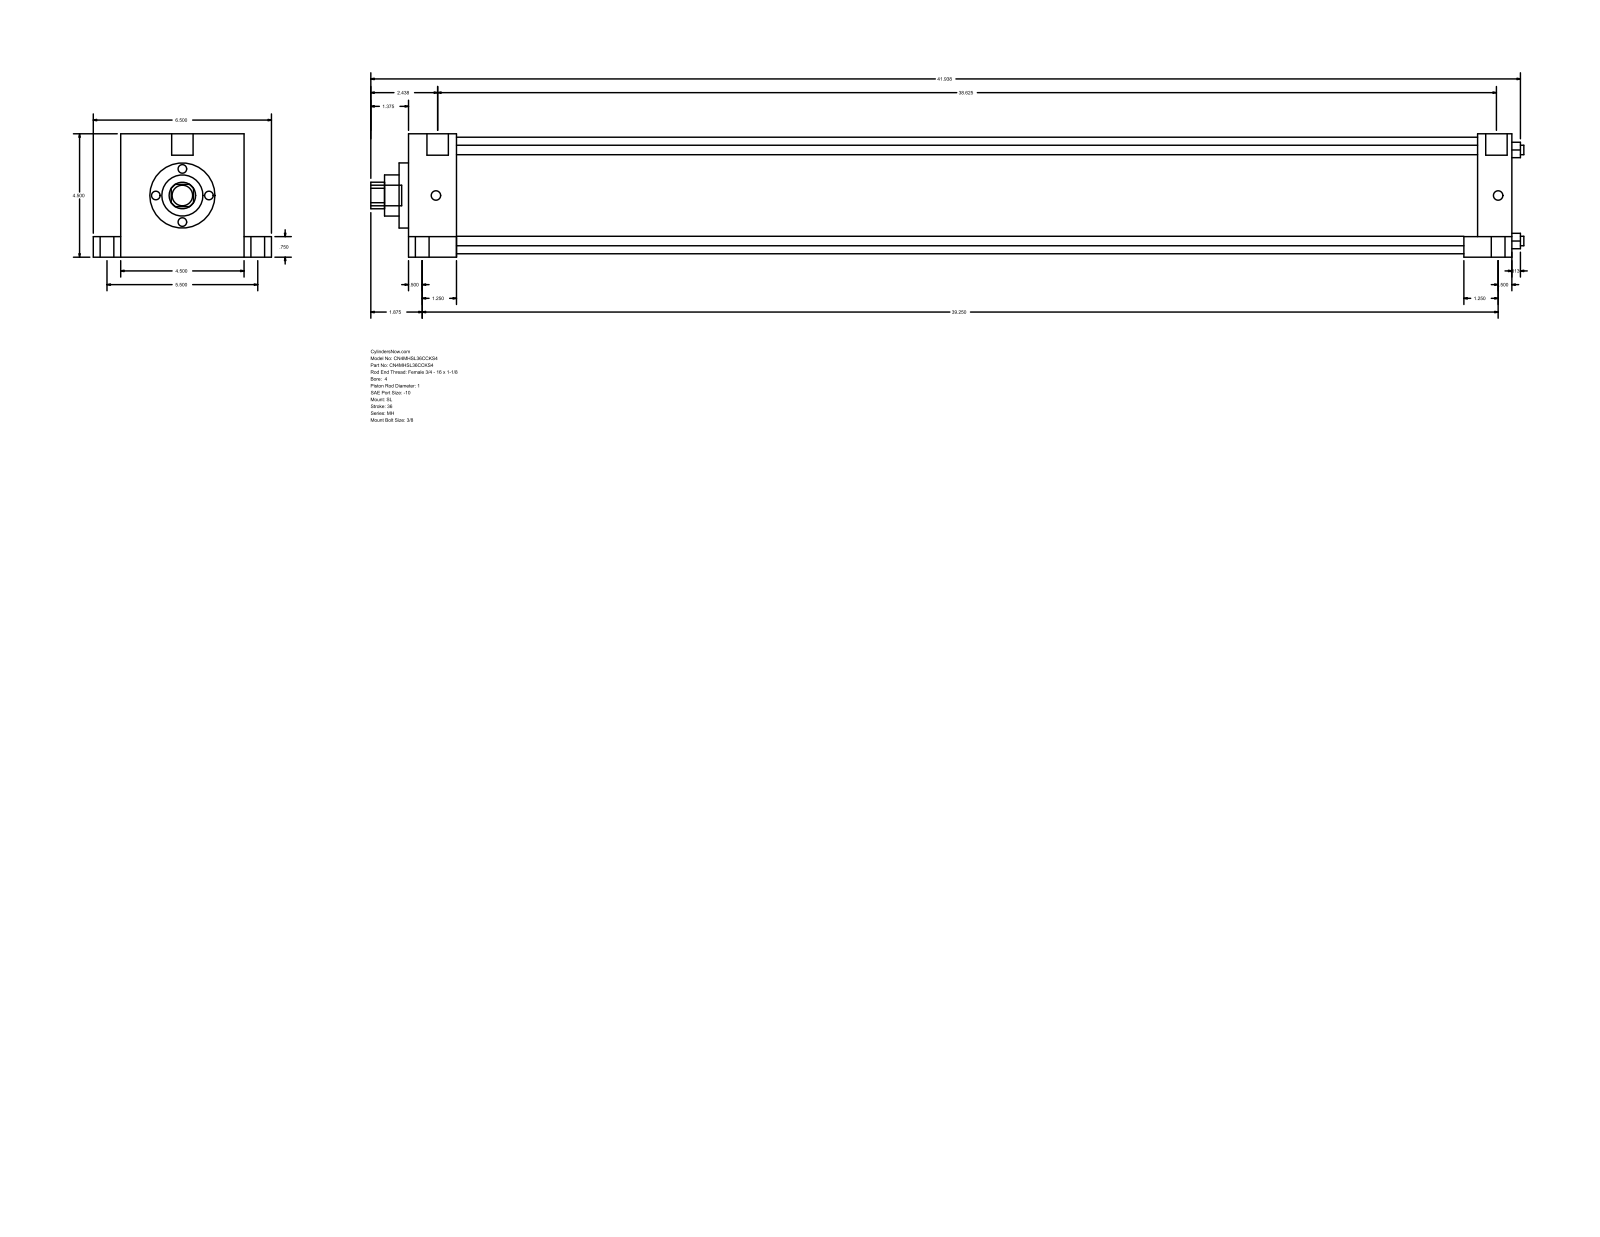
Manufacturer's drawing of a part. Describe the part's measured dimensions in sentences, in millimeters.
The part is named "MH_SL__0400_1". Its 3-D file was written by "GSSL Pune (CONFIG_CONTROL_DESIGN)". It is 0 solids with 110 faces: 77 planar, 33 cylindrical and 0 other. Overall it measures 1068.39 by 165.1 by 114.3 millimeters. Round holes: 4 of diameter 8.76, 1 of diameter 25.4, 1 of diameter 38.1, 1 of diameter 60.33, 1 of diameter 107.95. Round bosses or shafts: 5 of diameter 19.05, 4 of diameter 12.7, 4 of diameter 8.73, 2 of diameter 19.84. Partial cylindrical surfaces (rounded edges, fillets, slot ends): 1 of radius 12.29. The main face-to-face distances are 114.3, 1022.36, 44.46, 977.9, 990.61, 946.15, 31.75, 25.4, 139.7, 19.05. The hole center spacings are 59.62, 84.32, 119.25.
